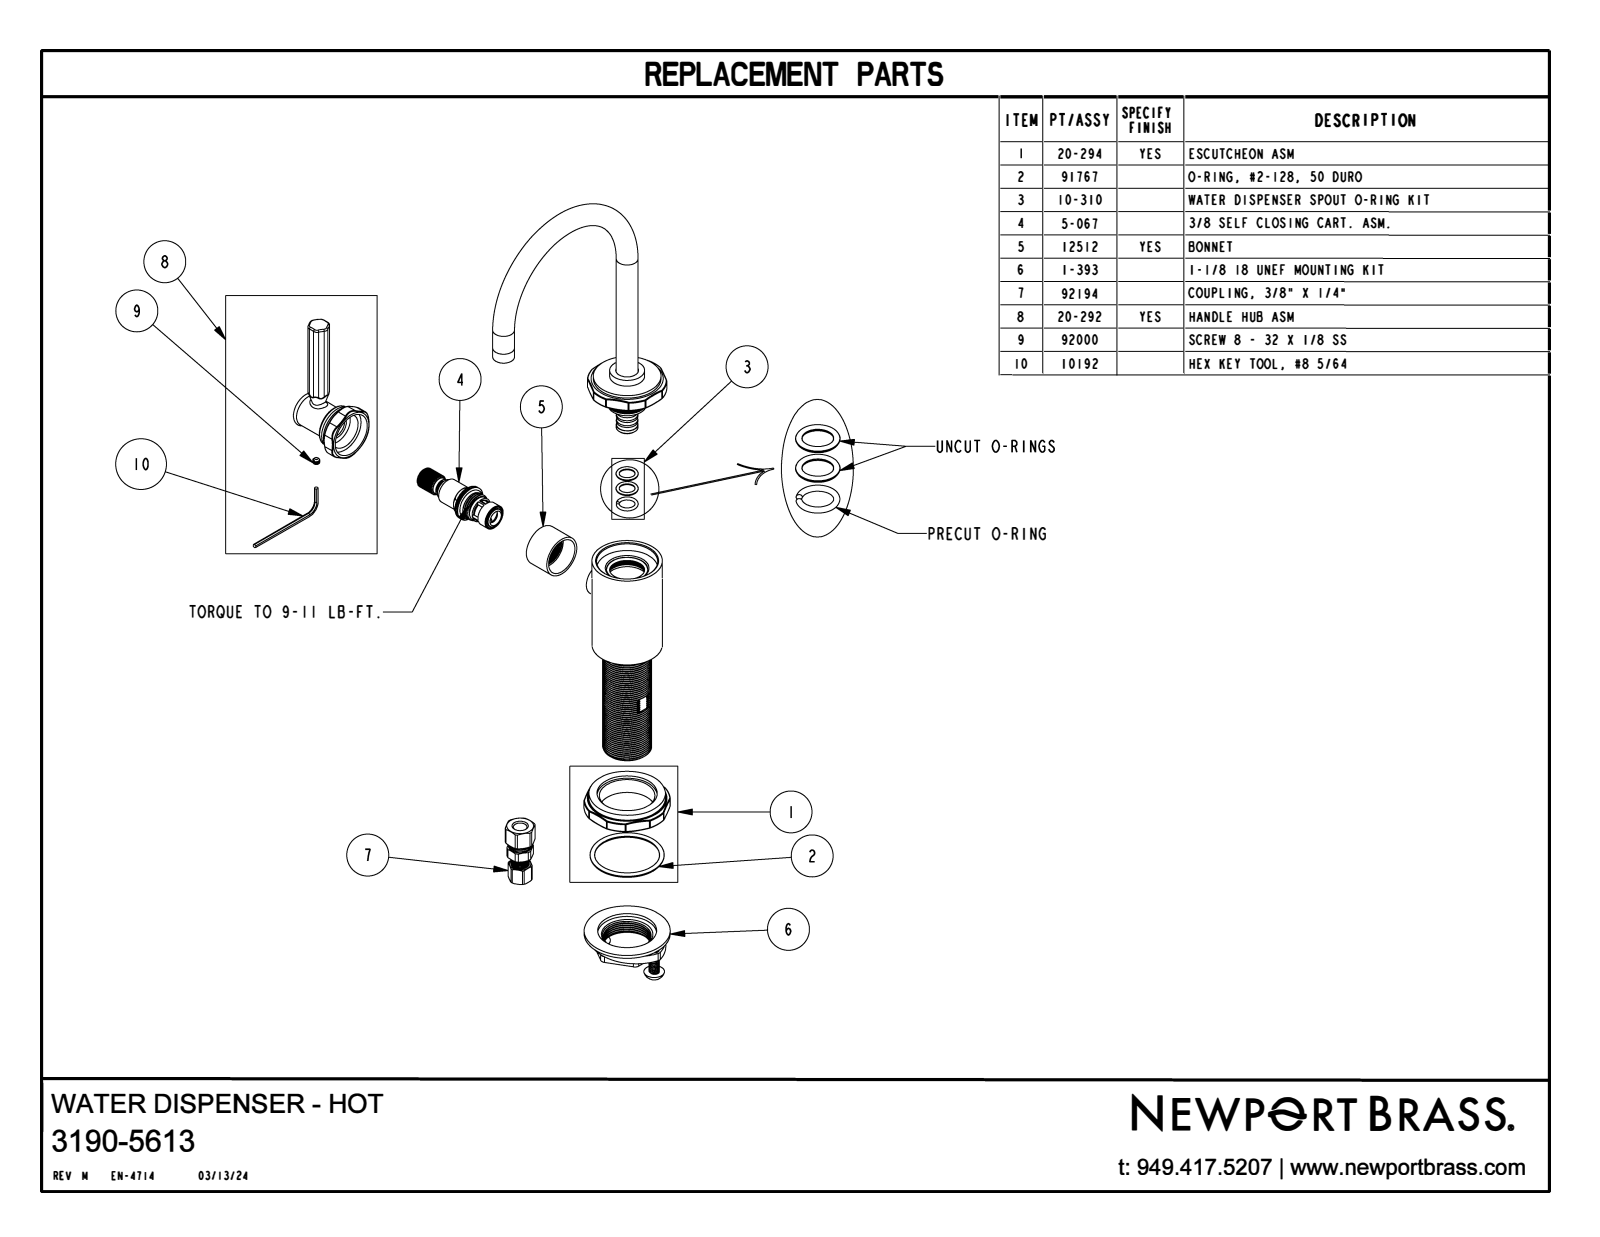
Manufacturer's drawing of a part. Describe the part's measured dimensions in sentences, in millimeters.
The part is named "3190-5613". Its 3-D file was written by "CREO PARAMETRIC BY PTC INC, 2018400 (CONFIG_CONTROL_DESIGN)". It is 1 solid with 306 faces: 36 planar, 66 cylindrical and 204 other. Overall it measures 235.6 by 132 by 90.1 millimeters. Its volume is 173 200 cubic millimeters and its surface area 32 030 square millimeters. Round holes: 1 of diameter 25.4. Round bosses or shafts: 2 of diameter 12.7, 1 of diameter 44.5, 1 of diameter 40.9, 1 of diameter 39.4, 1 of diameter 24.6, 1 of diameter 20.3, 1 of diameter 19.3. Partial cylindrical surfaces (rounded edges, fillets, slot ends): 24 of radius 2, 6 of radius 3, 6 of radius 7.9, 1 of radius 23.1, 1 of radius 25.1. The main face-to-face distances are 79.9, 11.9, 10.8, 69.1, 48, 44.1, 84, 73.2, 4.1, 37.8.
